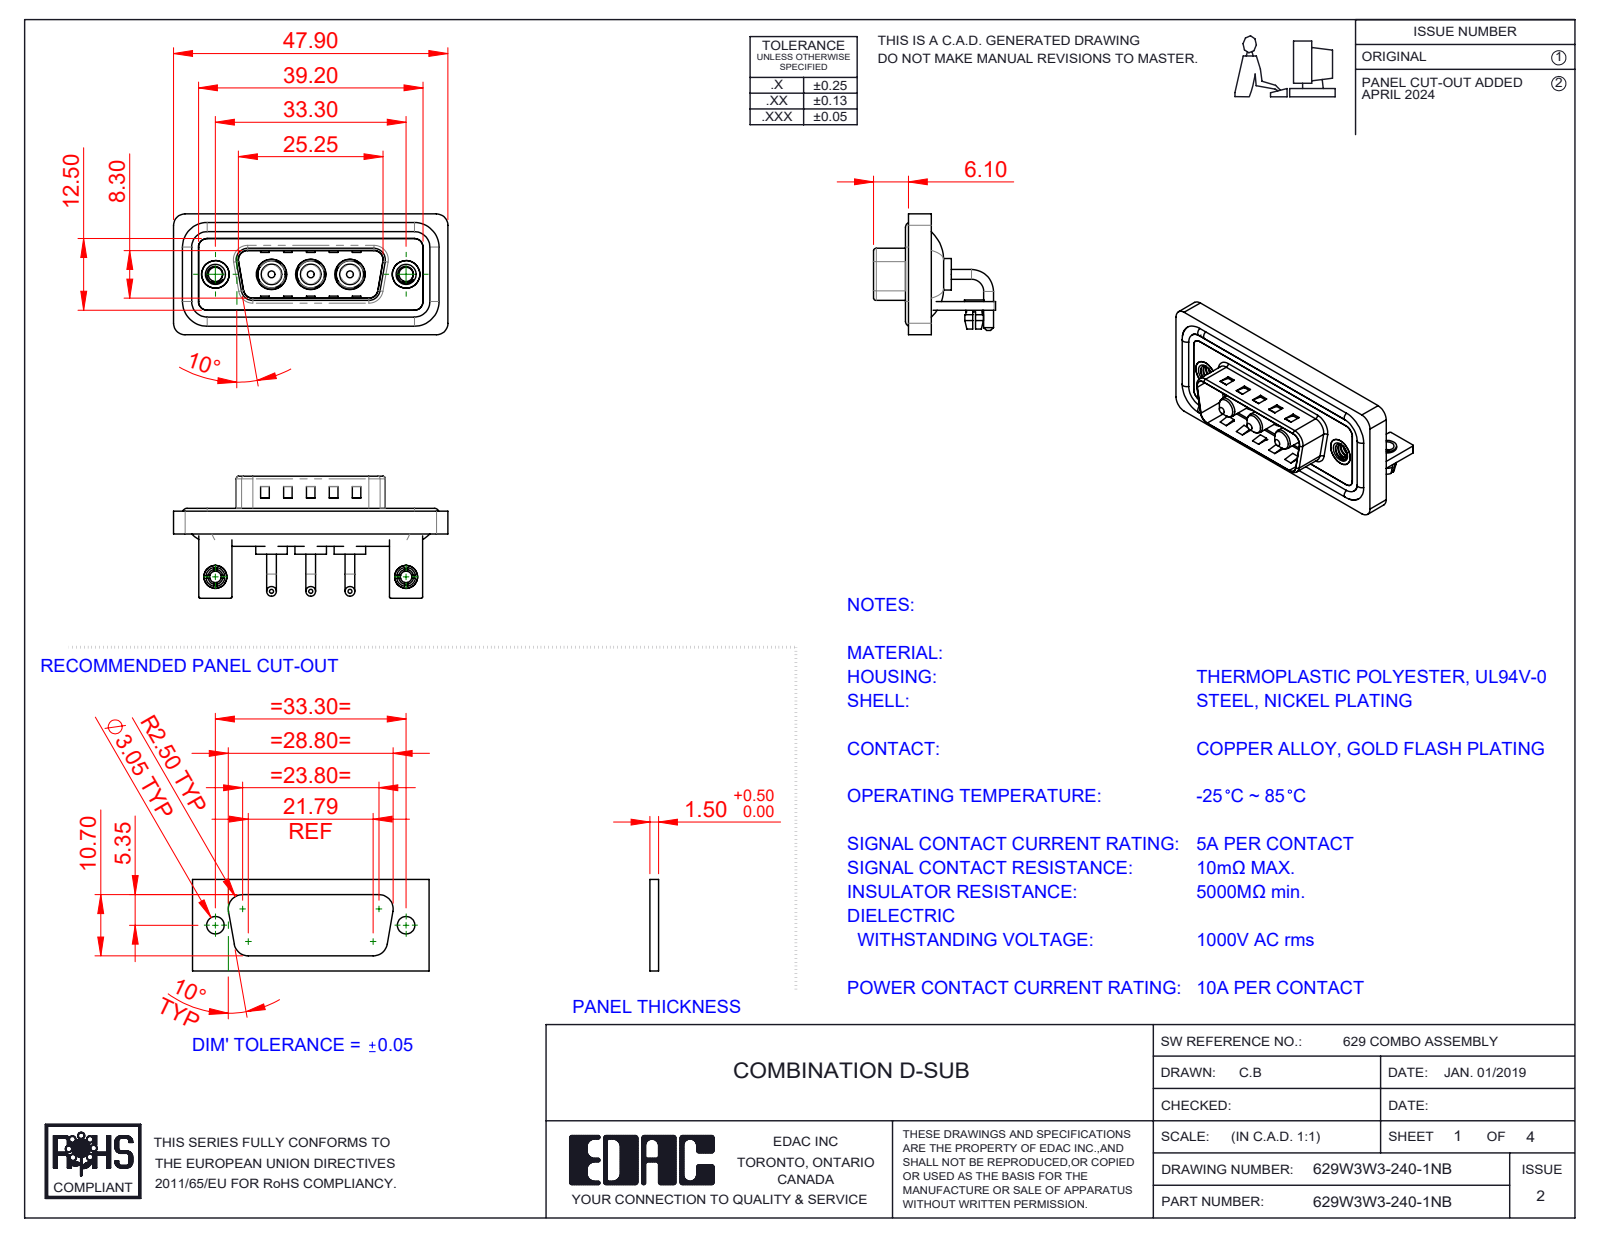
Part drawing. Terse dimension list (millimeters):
name: Power Pin_10A RA; 629Combo Stabilizer Bracket; 629Combo Threaded Rivet_B; 629Combo Board Lock (+5 more)
written by: SolidWorks 2023 (CONFIG_CONTROL_DESIGN)
unit: mm
bodies: 17 solids, 706 faces (275 planar, 297 cylindrical, 134 other)
size: 47.9 × 21.3 × 21.1
volume: 5 912 mm³; area: 9 682 mm²
holes: 4× ⌀2.5, 3× ⌀4.85, 3× ⌀5.3, 2× ⌀2, 2× ⌀3.2, 2× ⌀4, 2× ⌀4.8, 2× ⌀5
bosses: 6× ⌀1.7, 4× ⌀1.6, 3× ⌀5.5, 3× ⌀5.2, 3× ⌀4.75, 3× ⌀3.75, 3× ⌀3.6, 2× ⌀4.9
rounds: 21× R2, 18× R1.5, 16× R0.25, 9× R0.5, 8× R1.6, 4× R0.6, 4× R0.65, 4× R0.9
face distances: 0.4, 1.5, 0.8, 2.9, 1.1, 2.1, 3.7, 1.6, 1.2, 4.5
hole spacings: 6.85, 9.8, 16.65, 23.5, 33.3, 13.7
